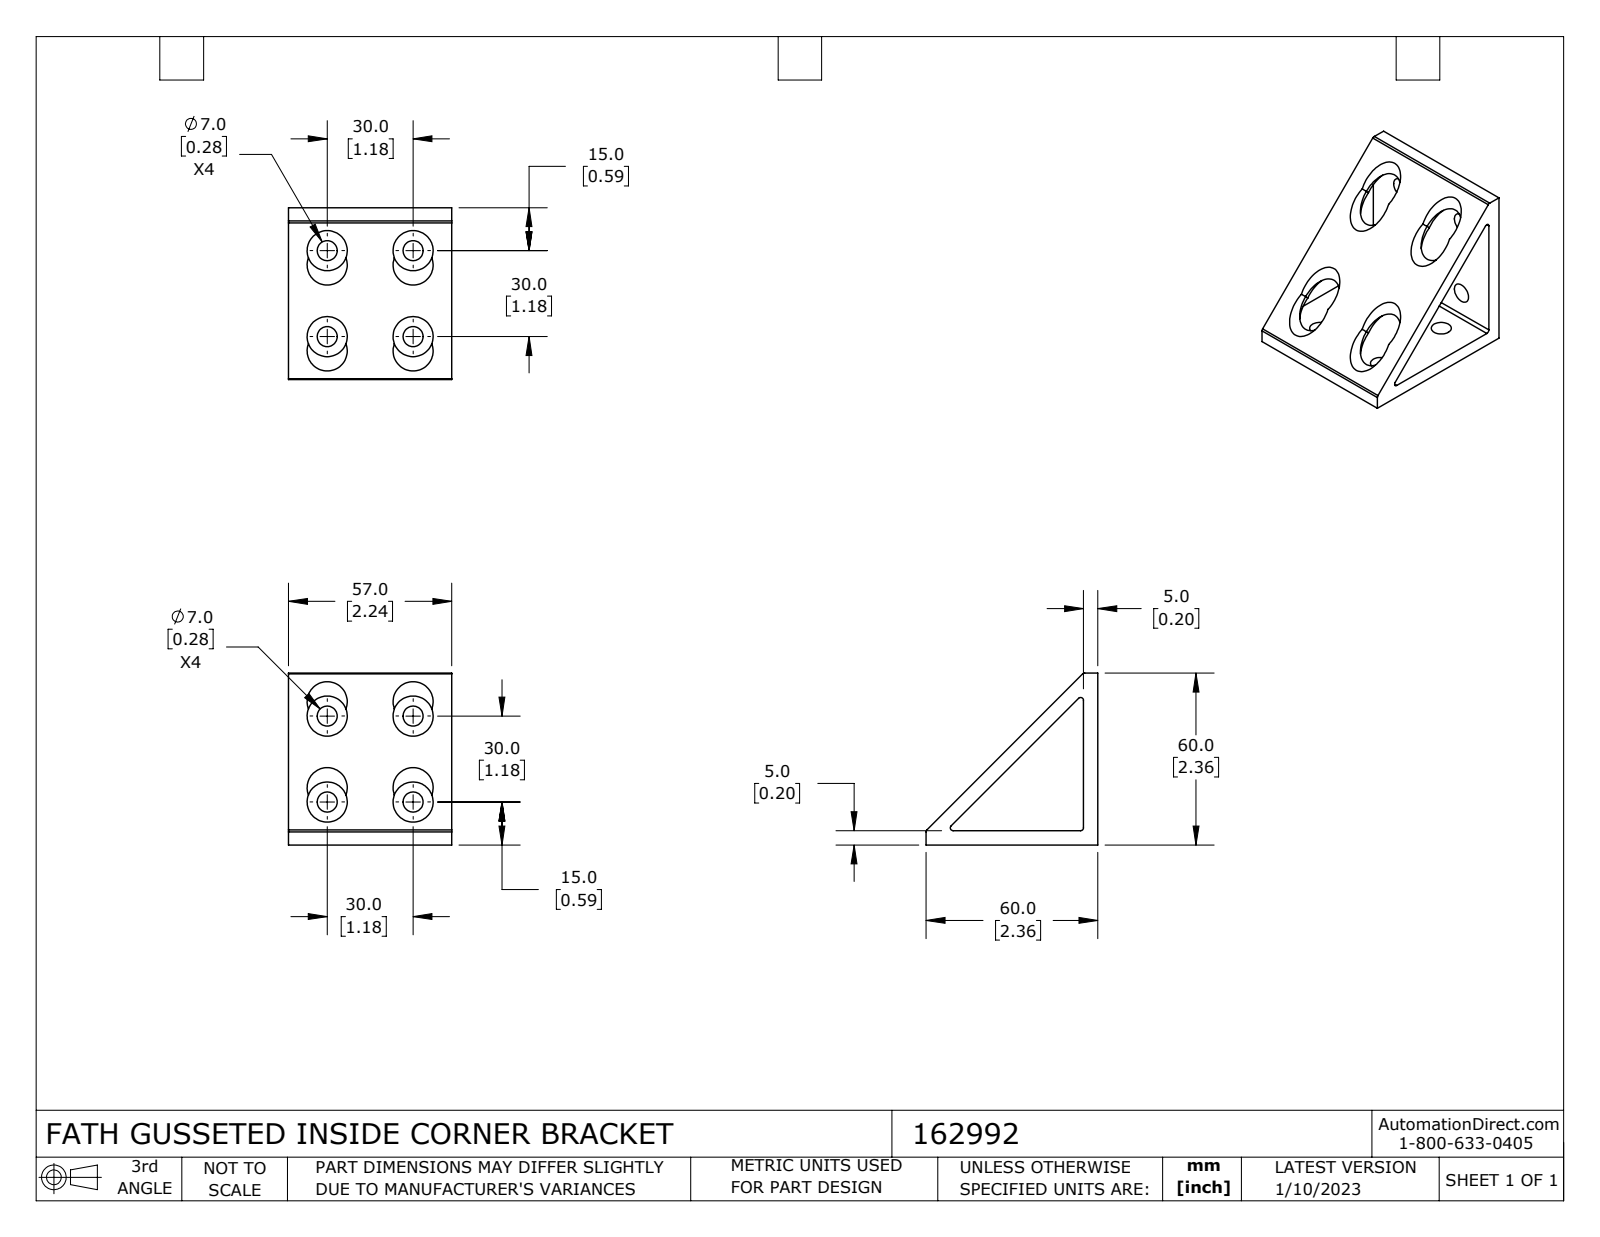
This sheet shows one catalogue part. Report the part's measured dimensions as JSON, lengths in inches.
{"part_name": "162992", "step_written_by": "SolidWorks 2021 (CONFIG_CONTROL_DESIGN)", "units": "inches", "bodies": {"solids": 1, "faces": 83, "planar": 10, "cylindrical": 73, "other": 0}, "overall_size": [2.362, 2.362, 2.244], "volume_in3": 2.865, "surface_area_in2": 34.25, "round_holes": [[0.276, 8], [0.551, 8]], "partial_cylinders_radius": [[0.039, 5]], "face_to_face_distances": [0.197, 0.196, 2.244, 2.362, 2.165], "hole_center_spacings": [1.181, 1.67]}
